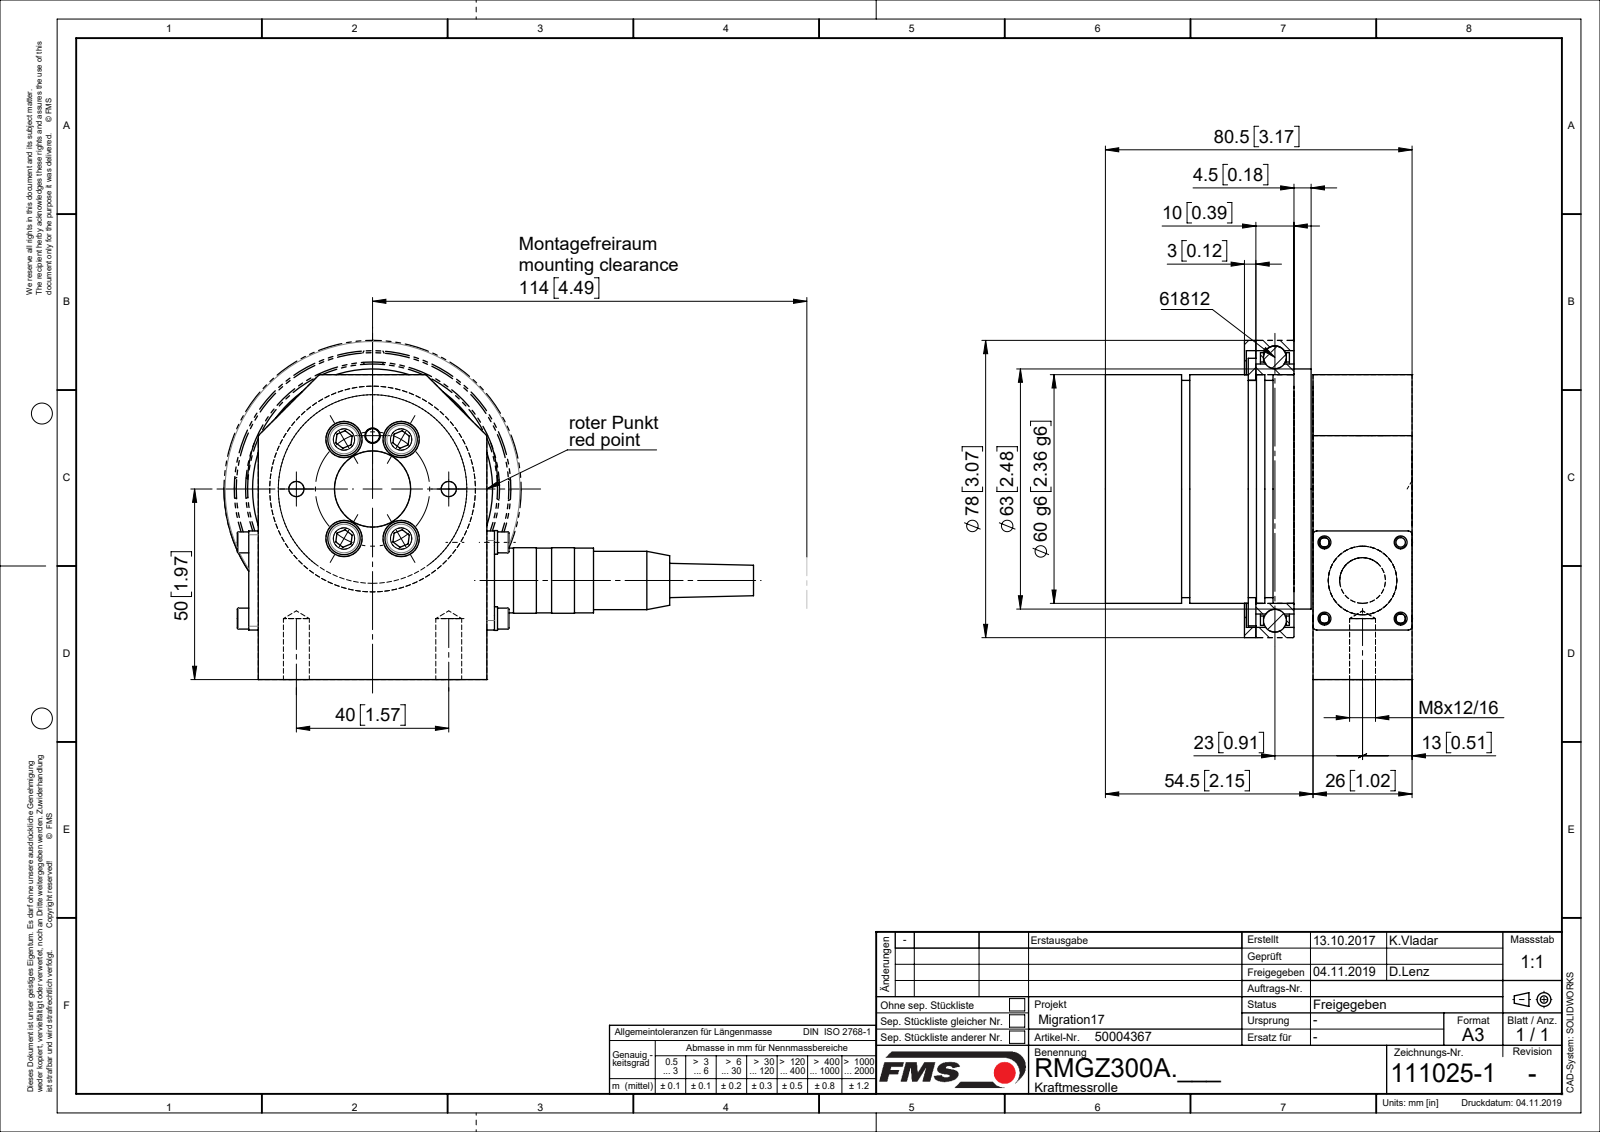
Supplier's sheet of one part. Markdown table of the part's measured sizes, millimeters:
| quantity | value |
| --- | --- |
| part name | R1110251; R51047; R1110253; I-6KT_SCHRAUBE_M5X8 (+8 more) |
| STEP written by | Mechanical Desktop 2009 (CONFIG_CONTROL_DESIGN) |
| units | millimeters |
| bodies | 27 solids, 532 faces (142 planar, 262 cylindrical, 128 other) |
| overall size | 140.5 × 90.5 × 80.5 |
| volume | 257 561 mm³ |
| surface area | 96 806 mm² |
| round holes (diameter × count) | 4 × 5, 2.6 × 4, 3.2 × 4, 3.4 × 4, 5.6 × 4, 9 × 4, 9.5 × 4, 7.15 × 2, 5 × 1, 12 × 1, 15 × 1, 18 × 1 |
| round bosses / shafts (diameter × count) | 1.5 × 5, 8 × 4, 5.5 × 4, 5 × 4, 3 × 4, 81 × 1, 78 × 1, 68.6 × 1 |
| partial cylindrical surfaces (radius × count) | 1 × 4, 2.5 × 4 |
| main face-to-face distances | 35, 12.5, 3, 32, 44, 17, 2.5, 47.5, 37.5, 0.5 |
| hole center spacings | 15, 14.14, 20, 7.57, 25.98, 28.01, 28.28, 30 |
